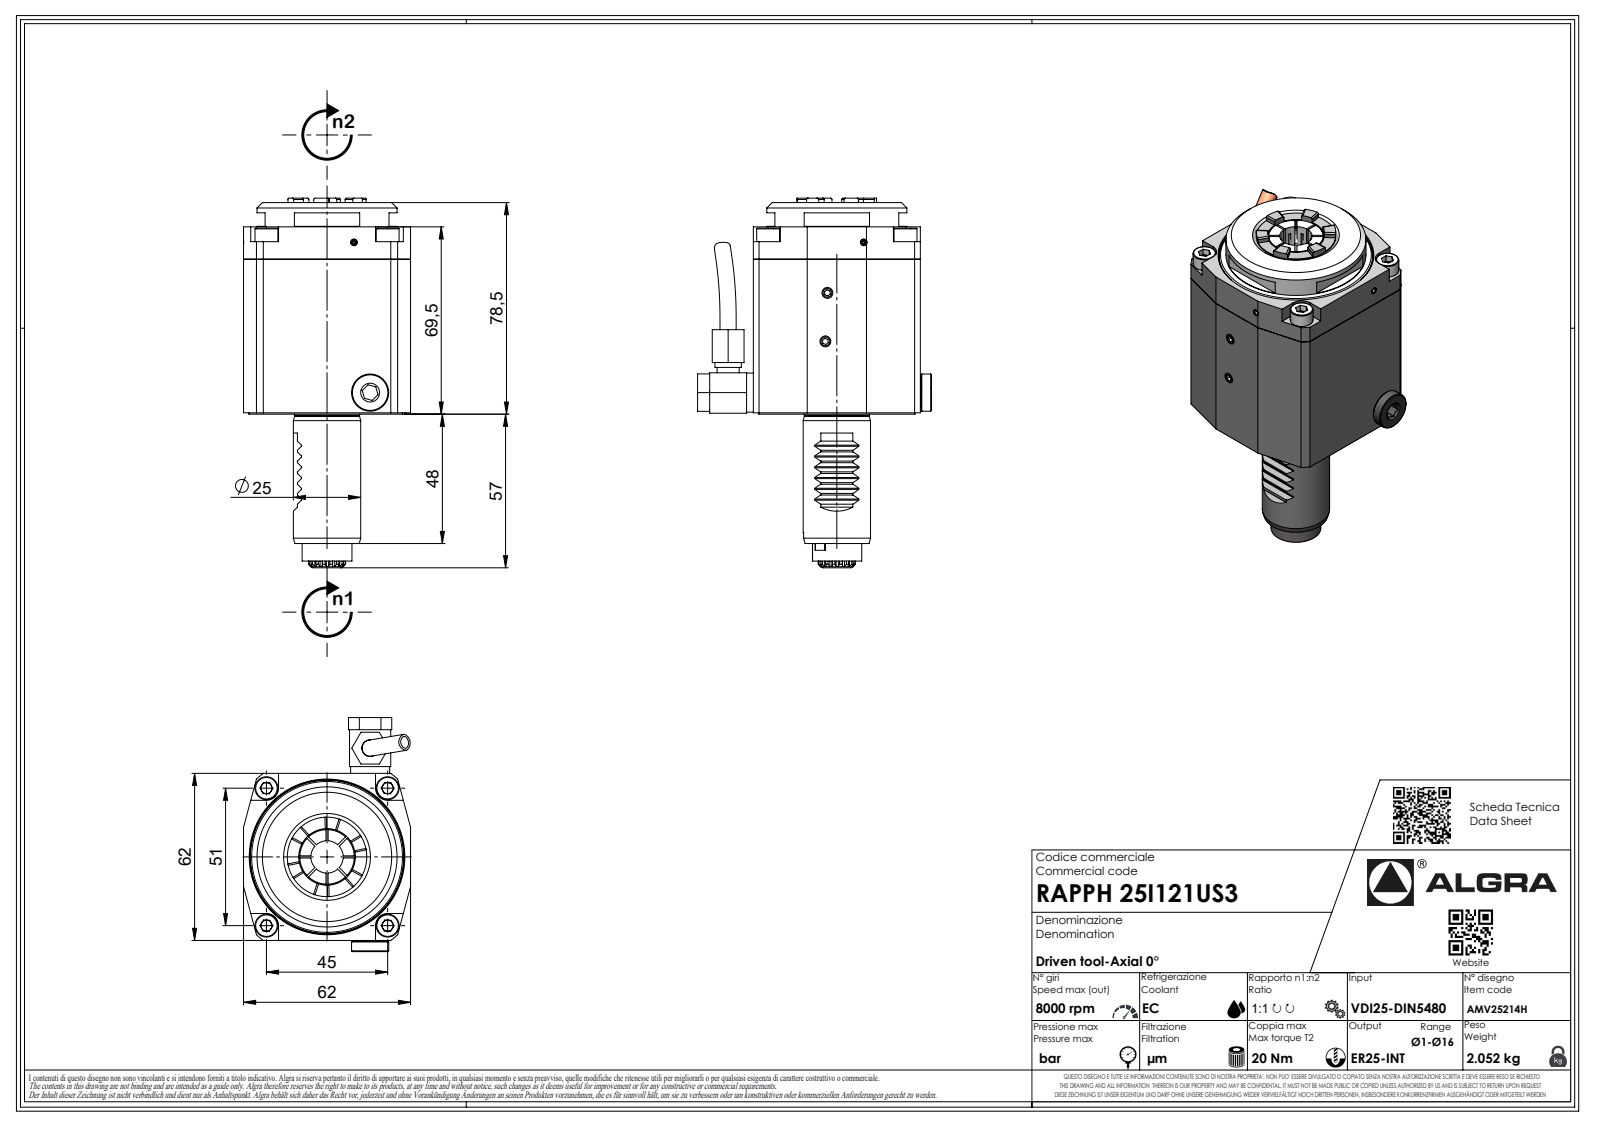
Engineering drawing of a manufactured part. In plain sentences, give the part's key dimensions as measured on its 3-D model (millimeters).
The part is named "RAPPH25I121US3". Its 3-D file was written by "SolidWorks 2023 (AUTOMOTIVE_DESIGN)". It is 1 solid with 706 faces: 427 planar, 135 cylindrical and 144 other. Overall it measures 137.15 by 86.85 by 62 millimeters. Its volume is 297 498 cubic millimeters and its surface area 35 100 square millimeters. Round holes: 1 of diameter 2.1, 1 of diameter 18.7, 1 of diameter 22. Round bosses or shafts: 1 of diameter 58, 1 of diameter 52, 1 of diameter 25, 1 of diameter 24.1, 1 of diameter 18.5, 1 of diameter 14.5, 1 of diameter 13.8, 1 of diameter 12. Partial cylindrical surfaces (rounded edges, fillets, slot ends): 8 of radius 35, 7 of radius 0.33, 7 of radius 0.52, 7 of radius 3.7, 6 of radius 0.3, 4 of radius 4.5, 1 of radius 0.21, 1 of radius 3.25. The main face-to-face distances are 62, 65.58, 78.5, 9, 69.5, 0.5, 69, 78, 65.59, 8.
